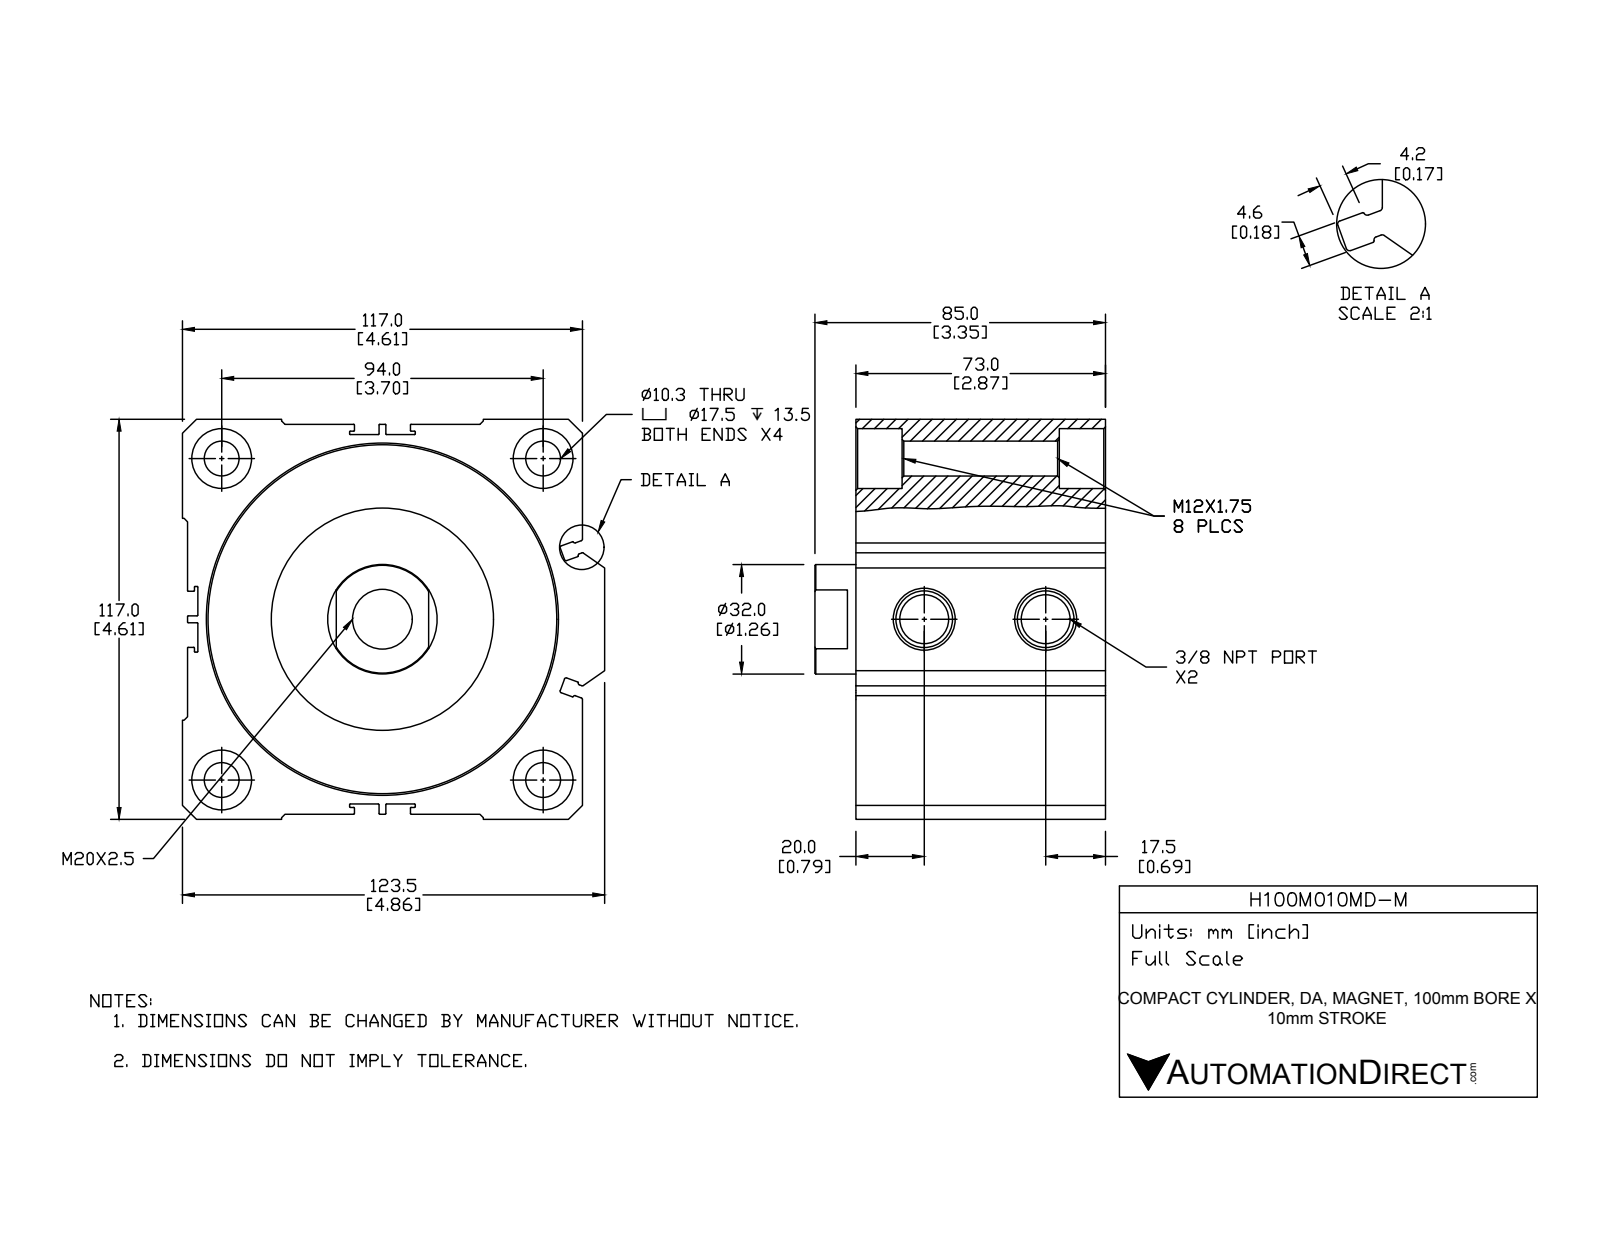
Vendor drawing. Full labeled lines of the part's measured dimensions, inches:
Part name (STEP PRODUCT): H100M010MD-M; H100M010MD-M-PISTON; H100M010MD-M-BODY
STEP written by: SolidWorks 2015 (CONFIG_CONTROL_DESIGN)
Units: inches
Bodies: 2 solids, 261 faces (105 planar, 103 cylindrical, 53 other)
Overall size (bounding box): 4.862 × 4.606 × 3.346
Volume: 48.62 in³ · Surface area: 222 in²
Round holes (diameter × count): ⌀0.689 ×5, ⌀0.402 ×4, ⌀0.562 ×2, ⌀1.26 ×1, ⌀2.559 ×1, ⌀3.937 ×1, ⌀4.016 ×1
Round bosses / shafts (diameter × count): ⌀1.535 ×1
Partial cylindrical surfaces — rounded edges, fillets, slot ends (radius × count): R0.008 ×40, R0.02 ×12
Main face-to-face distances: 0.059, 4.547, 0.421, 4.606, 1.094, 1.516, 0.492, 1.587, 2.008, 0.472
Hole centre spacings: 2.617, 3.701, 5.234, 1.398
